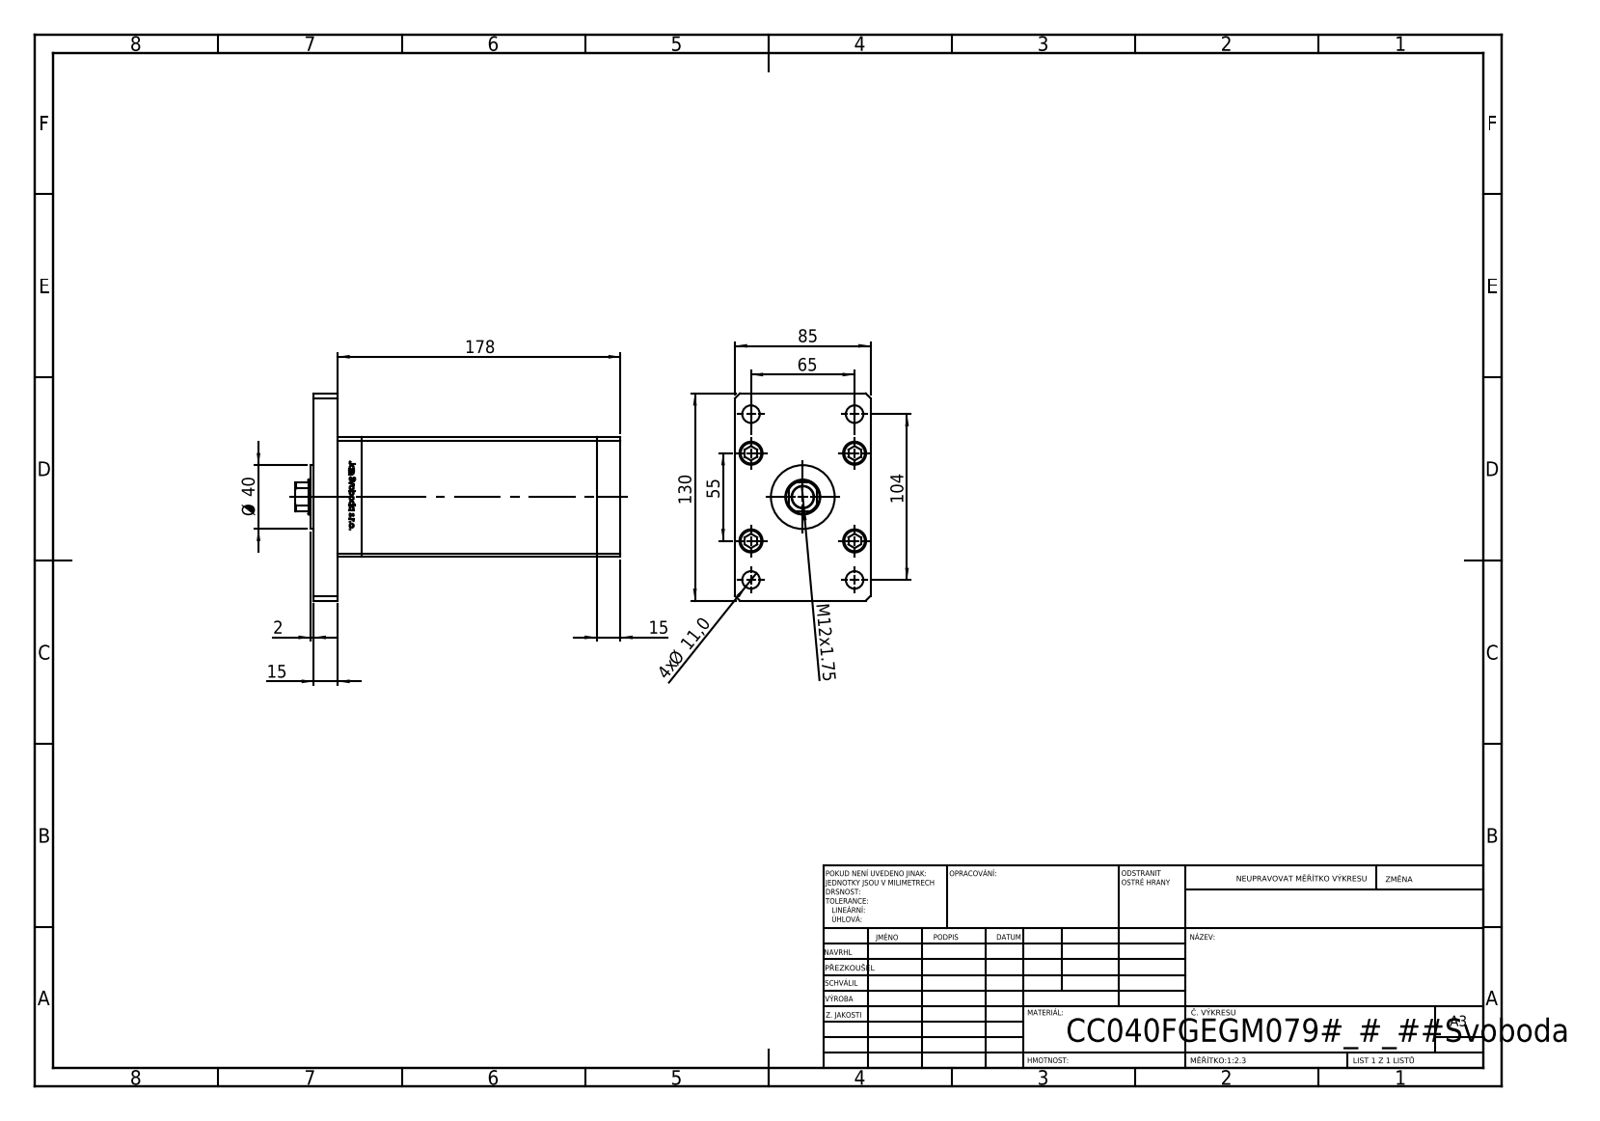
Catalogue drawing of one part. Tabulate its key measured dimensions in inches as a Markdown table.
| quantity | value |
| --- | --- |
| part name | V220C_FRONT_F; V220C_VC_F; V220C BACK_F; ALLEN BOLT (+2 more) |
| STEP written by | SolidWorks 2019 (CONFIG_CONTROL_DESIGN) |
| units | inches |
| bodies | 19 solids, 1310 faces (517 planar, 187 cylindrical, 606 other) |
| overall size | 8.031 × 5.118 × 3.346 |
| volume | 70.79 in³ |
| surface area | 307.4 in² |
| round holes (diameter × count) | 0.433 × 9, 0.61 × 5, 0.394 × 4, 0.571 × 4, 0.079 × 2, 0.518 × 2, 0.531 × 1, 0.866 × 1, 0.925 × 1 |
| round bosses / shafts (diameter × count) | 0.315 × 9, 0.571 × 5, 1.575 × 1 |
| partial cylindrical surfaces (radius × count) | 0.037 × 2, 0.413 × 1 |
| main face-to-face distances | 0.591, 3.346, 6.398, 6.988, 2.953, 1.181, 5.807, 7.579, 0.413, 1.083 |
| hole center spacings | 1.102, 0.965, 1.676, 2.414, 2.559, 2.735, 3.13, 4.043 |
